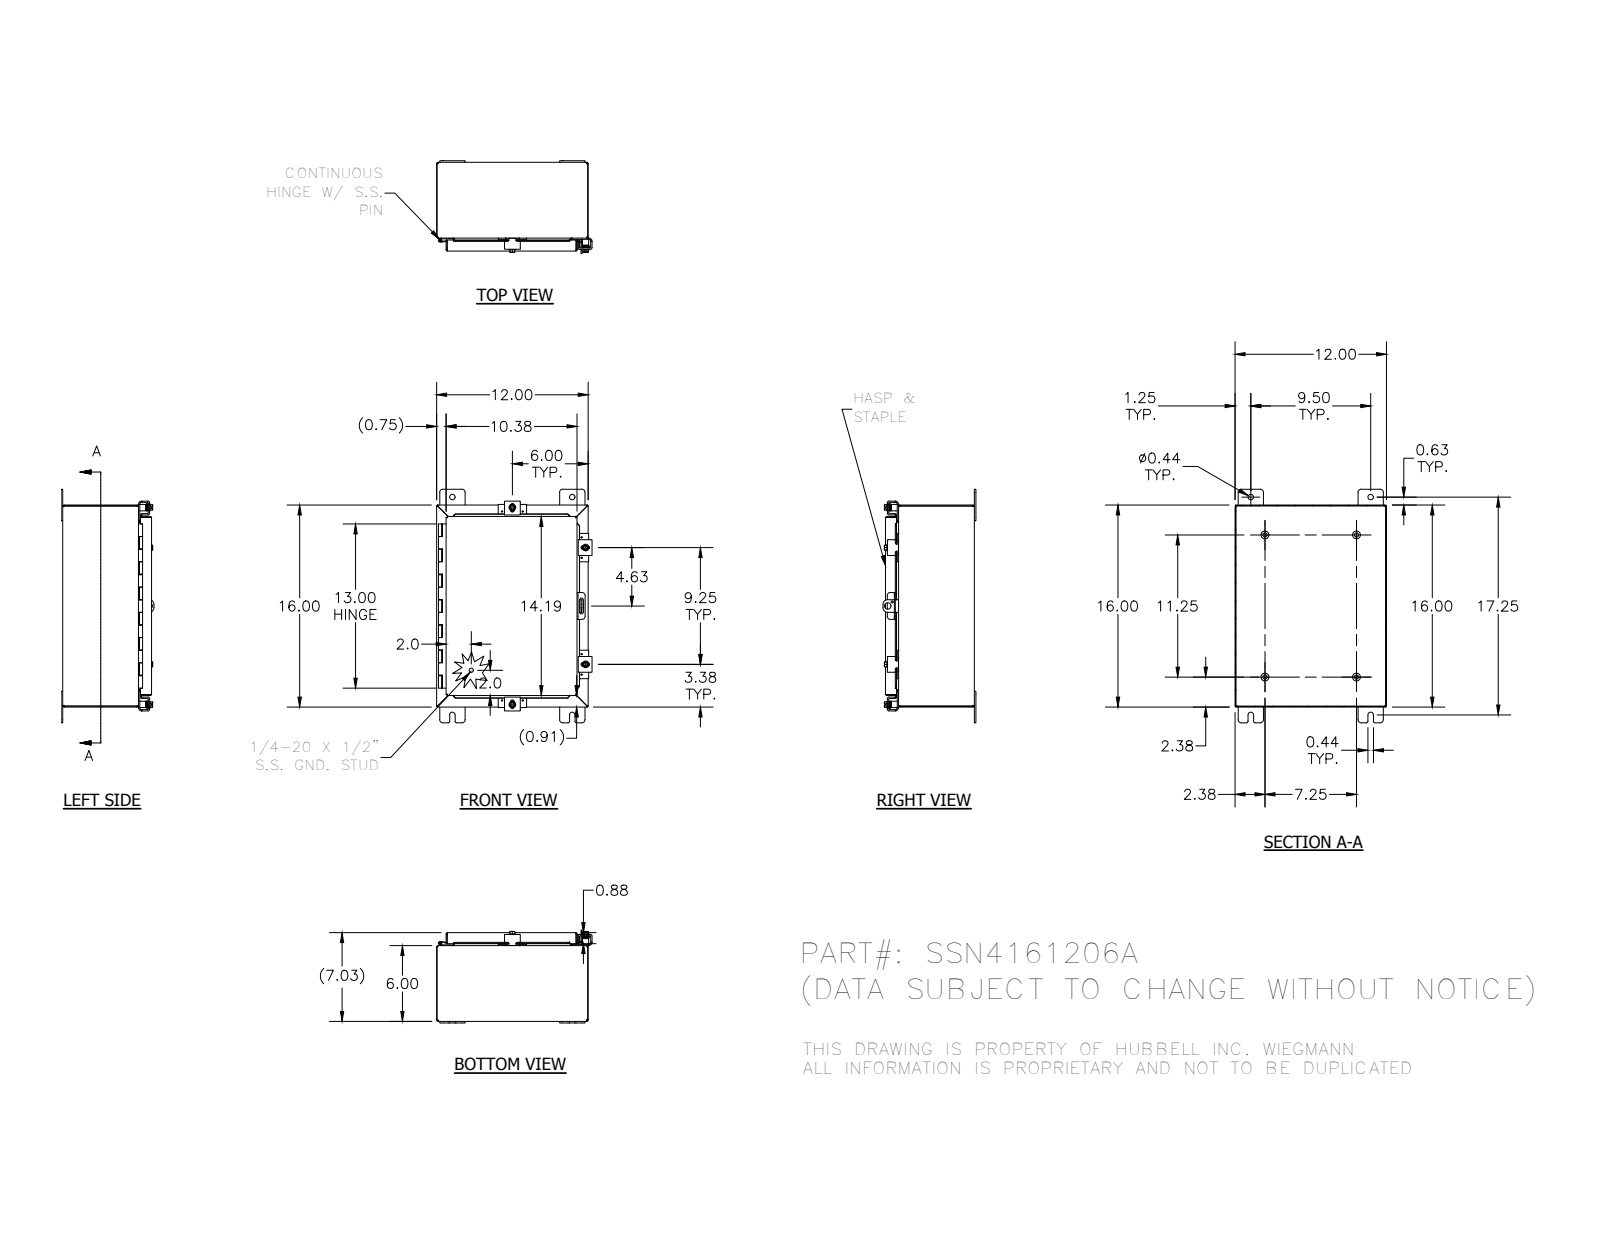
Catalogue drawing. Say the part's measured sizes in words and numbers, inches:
The part is named "SSN4161206A; 30818_1; HFW30825-3_1; 328136_1 (+8 more)". Its 3-D file was written by "SolidWorks 2014 (AUTOMOTIVE_DESIGN)". It is 37 solids with 1428 faces: 551 planar, 620 cylindrical and 257 other. Overall it measures 18.5 by 12.311 by 7.355 inches. Its volume is 73.01 cubic inches and its surface area 1 889 square inches. Round holes: 11 of diameter 0.11, 4 of diameter 0.211, 4 of diameter 0.281, 4 of diameter 0.3, 4 of diameter 0.438, 1 of diameter 0.125, 1 of diameter 0.156, 1 of diameter 0.5. Round bosses or shafts: 6 of diameter 0.25, 4 of diameter 0.625, 4 of diameter 0.52, 4 of diameter 0.5, 4 of diameter 0.35, 4 of diameter 0.33, 2 of diameter 0.115, 1 of diameter 0.337. Partial cylindrical surfaces (rounded edges, fillets, slot ends): 49 of radius 0.03, 33 of radius 0.125, 29 of radius 0.25, 23 of radius 0.031, 23 of radius 0.105, 11 of radius 0.062, 8 of radius 0.07, 8 of radius 0.141. The main face-to-face distances are 0.074, 7.002, 11.926, 6.928, 7.076, 15.926, 5.926, 1.076, 11.852, 12. The hole center spacings are 0.876, 15.311, 9.25, 0.779, 0.876, 1.625, 1.625, 3.828.
